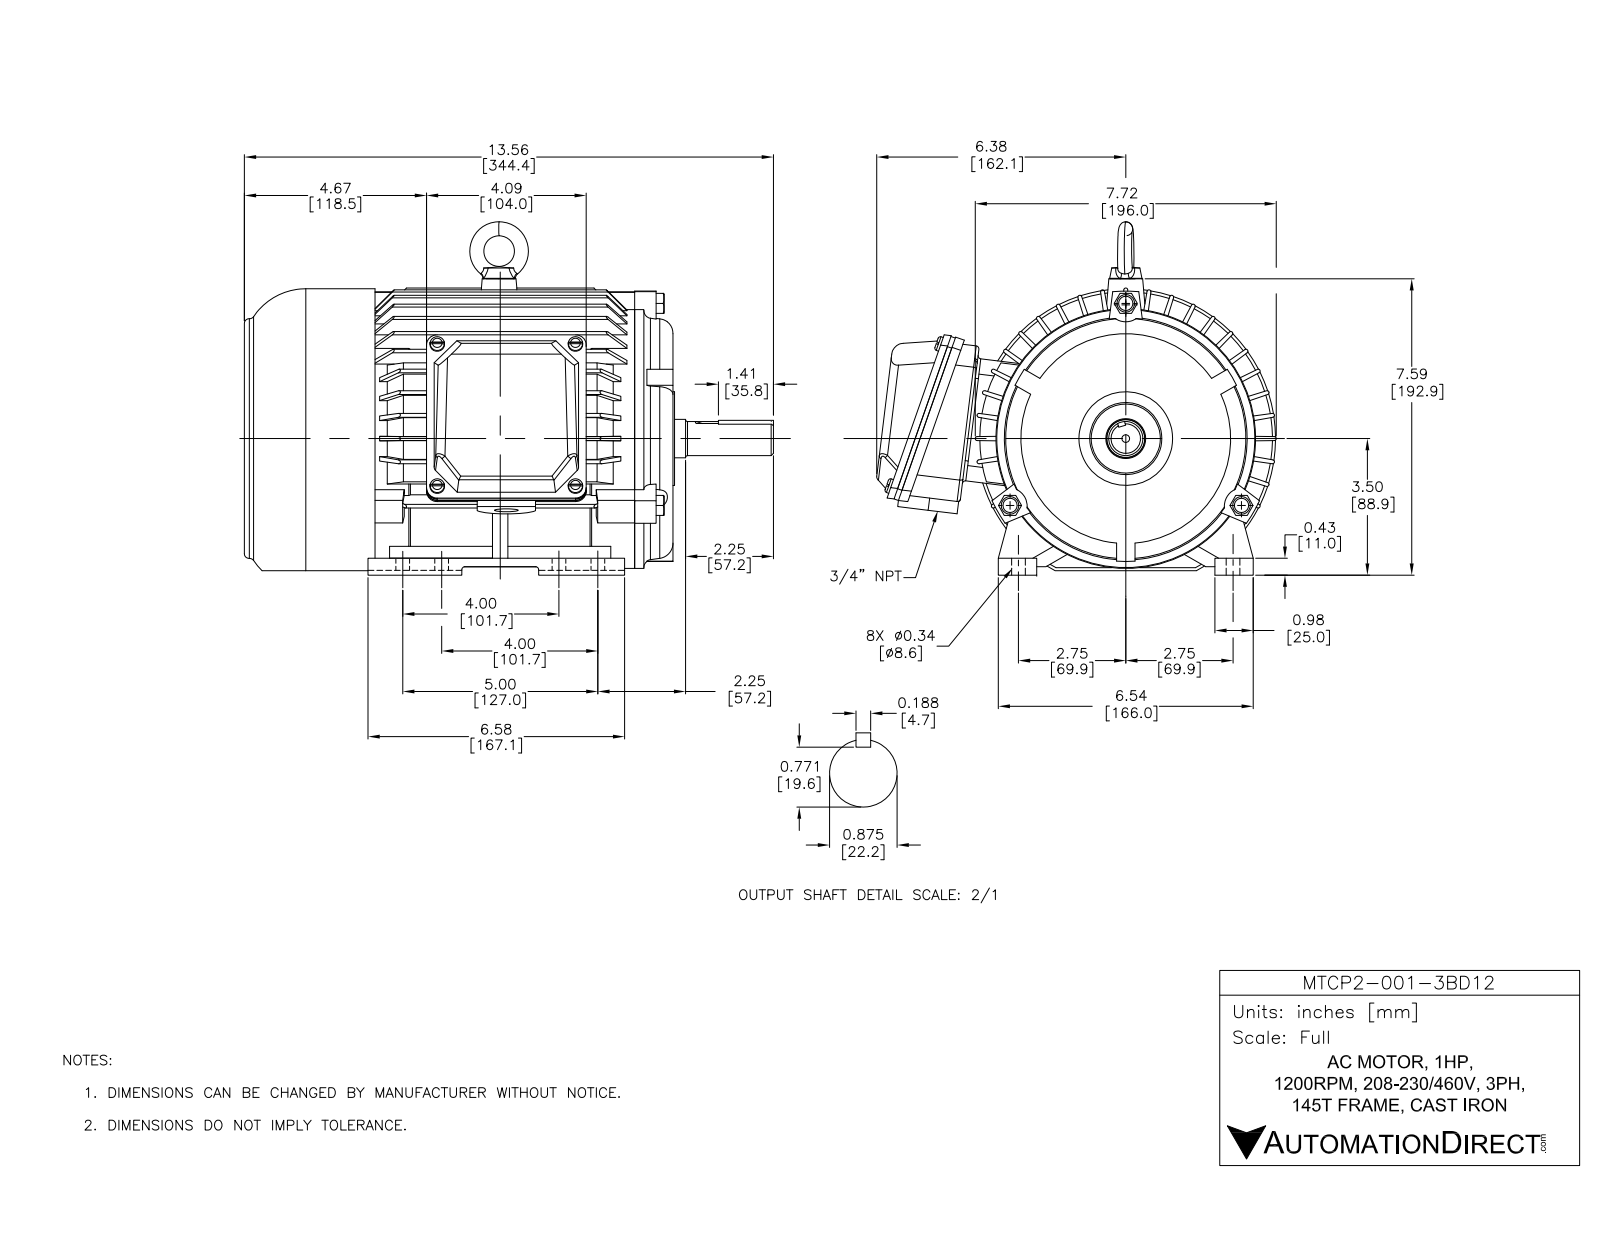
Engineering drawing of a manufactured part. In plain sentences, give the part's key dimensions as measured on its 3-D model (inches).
The part is named "PEWWE-145T". Its 3-D file was written by "SolidWorks 2017 (AUTOMOTIVE_DESIGN)". It is 14 solids with 1431 faces: 658 planar, 554 cylindrical and 219 other. Overall it measures 13.559 by 10.242 by 9.055 inches. Its volume is 298.1 cubic inches and its surface area 952.9 square inches. Round holes: 8 of diameter 0.228, 8 of diameter 0.354, 4 of diameter 0.165, 4 of diameter 0.197, 4 of diameter 0.326, 3 of diameter 0.362, 3 of diameter 0.394, 1 of diameter 0.268, 1 of diameter 0.276, 1 of diameter 0.315, 1 of diameter 0.61, 1 of diameter 0.984. Round bosses or shafts: 4 of diameter 0.315, 4 of diameter 0.197, 3 of diameter 0.283, 1 of diameter 7.677, 1 of diameter 7.52, 1 of diameter 6.654, 1 of diameter 6.575, 1 of diameter 6.22. Partial cylindrical surfaces (rounded edges, fillets, slot ends): 224 of radius 0.02, 26 of radius 0.05, 24 of radius 0.079, 16 of radius 0.276, 10 of radius 0.118, 4 of radius 0.236, 4 of radius 0.394, 3 of radius 0.472. The main face-to-face distances are 6.89, 0.157, 0.079, 9.864, 2.974, 0.984, 10.927, 9.943, 3.053, 7.874. The hole center spacings are 3.543, 2.126, 3.858, 5.239, 0.157, 1, 2.132, 4.
